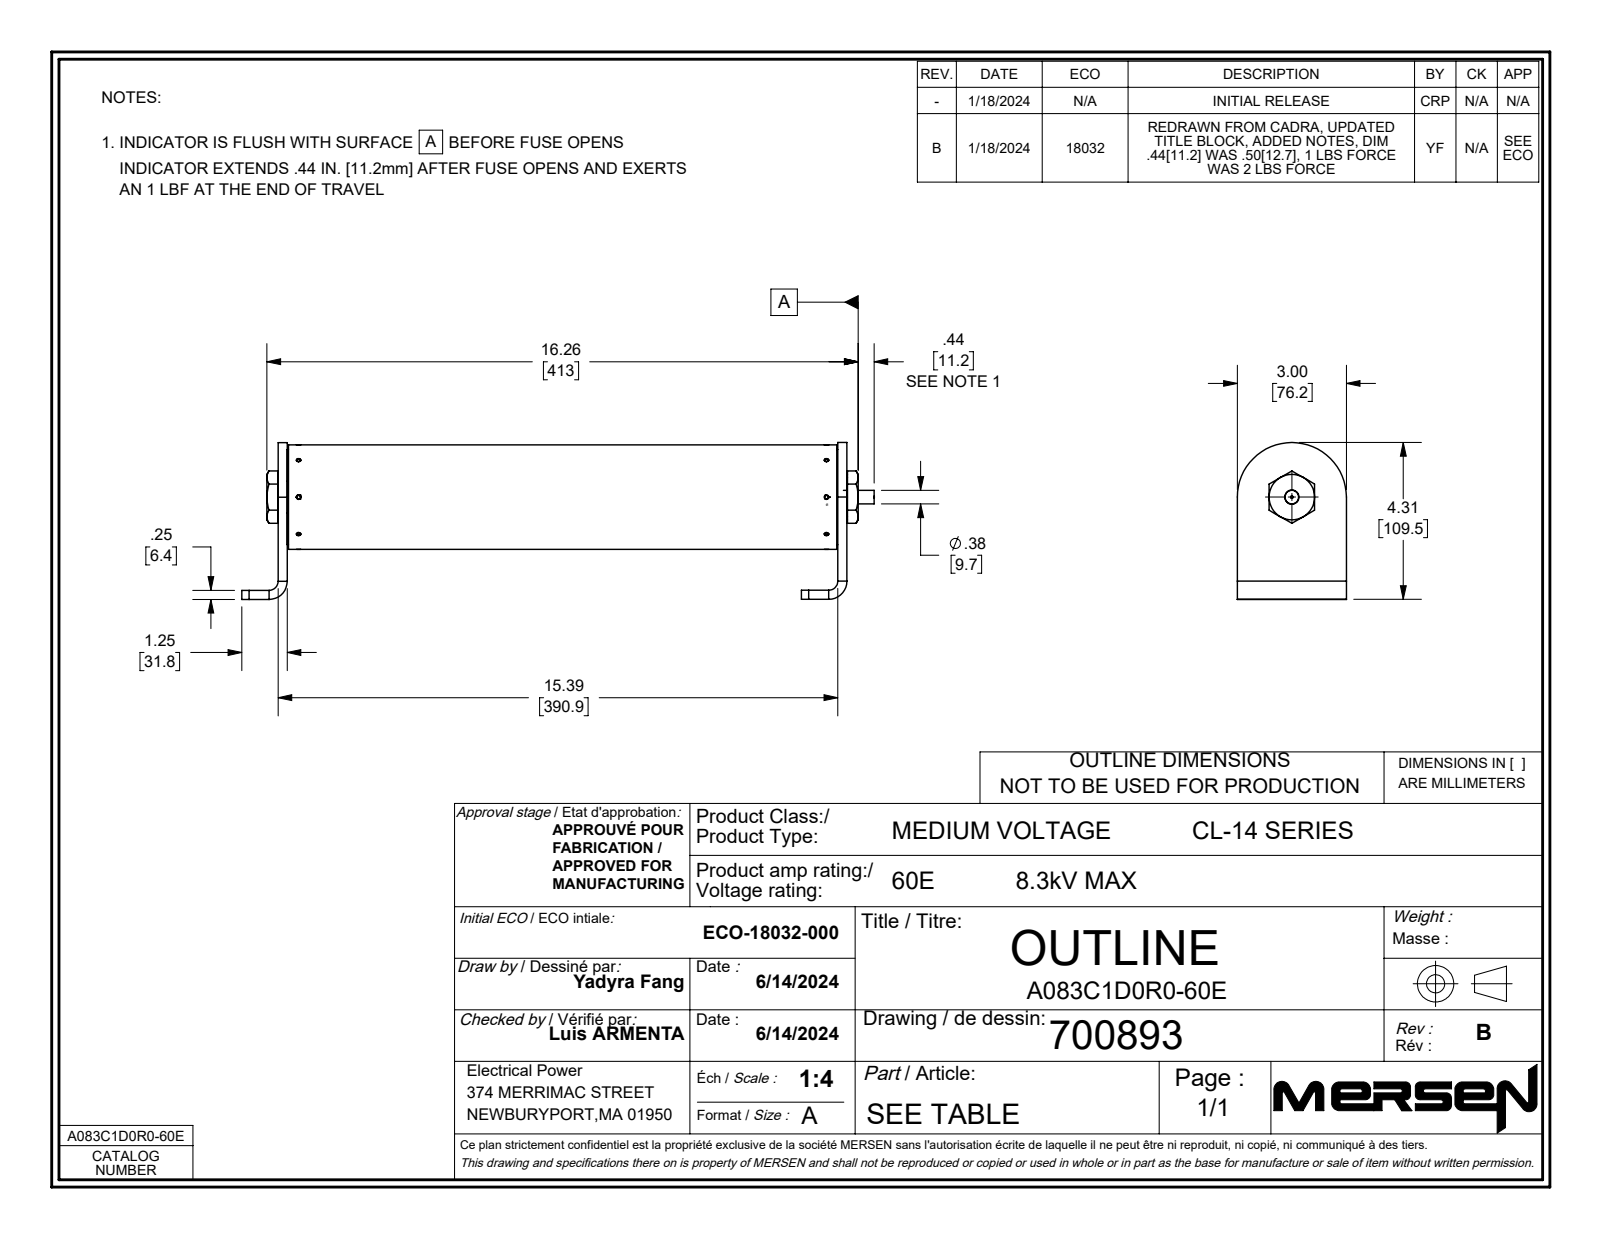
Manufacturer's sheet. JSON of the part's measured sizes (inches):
{"part_name": "700893; 9399_9399", "step_written_by": "SolidWorks 2021 (AUTOMOTIVE_DESIGN)", "units": "inches", "bodies": {"solids": 23, "faces": 1779, "planar": 451, "cylindrical": 748, "other": 580}, "overall_size": [16.952, 4.312, 3], "volume_in3": 24.93, "surface_area_in2": 346.8, "round_holes": [[0.125, 12], [0.906, 2], [0.02, 1], [0.063, 1], [0.146, 1], [0.189, 1], [0.391, 1], [0.465, 1], [0.512, 1], [2.625, 1]], "round_bosses_or_shafts": [[2.875, 1], [1.25, 1], [0.875, 1], [0.875, 1], [0.782, 1], [0.78, 1], [0.562, 1], [0.453, 1]], "partial_cylinders_radius": [[4, 61], [0.2, 4], [0.25, 2], [0.5, 2], [1.5, 2]], "face_to_face_distances": [0.25, 15.39, 15.64, 15.14, 0.248, 0.252, 0.591, 15.669, 1.25, 15.948], "hole_center_spacings": [14.518]}
